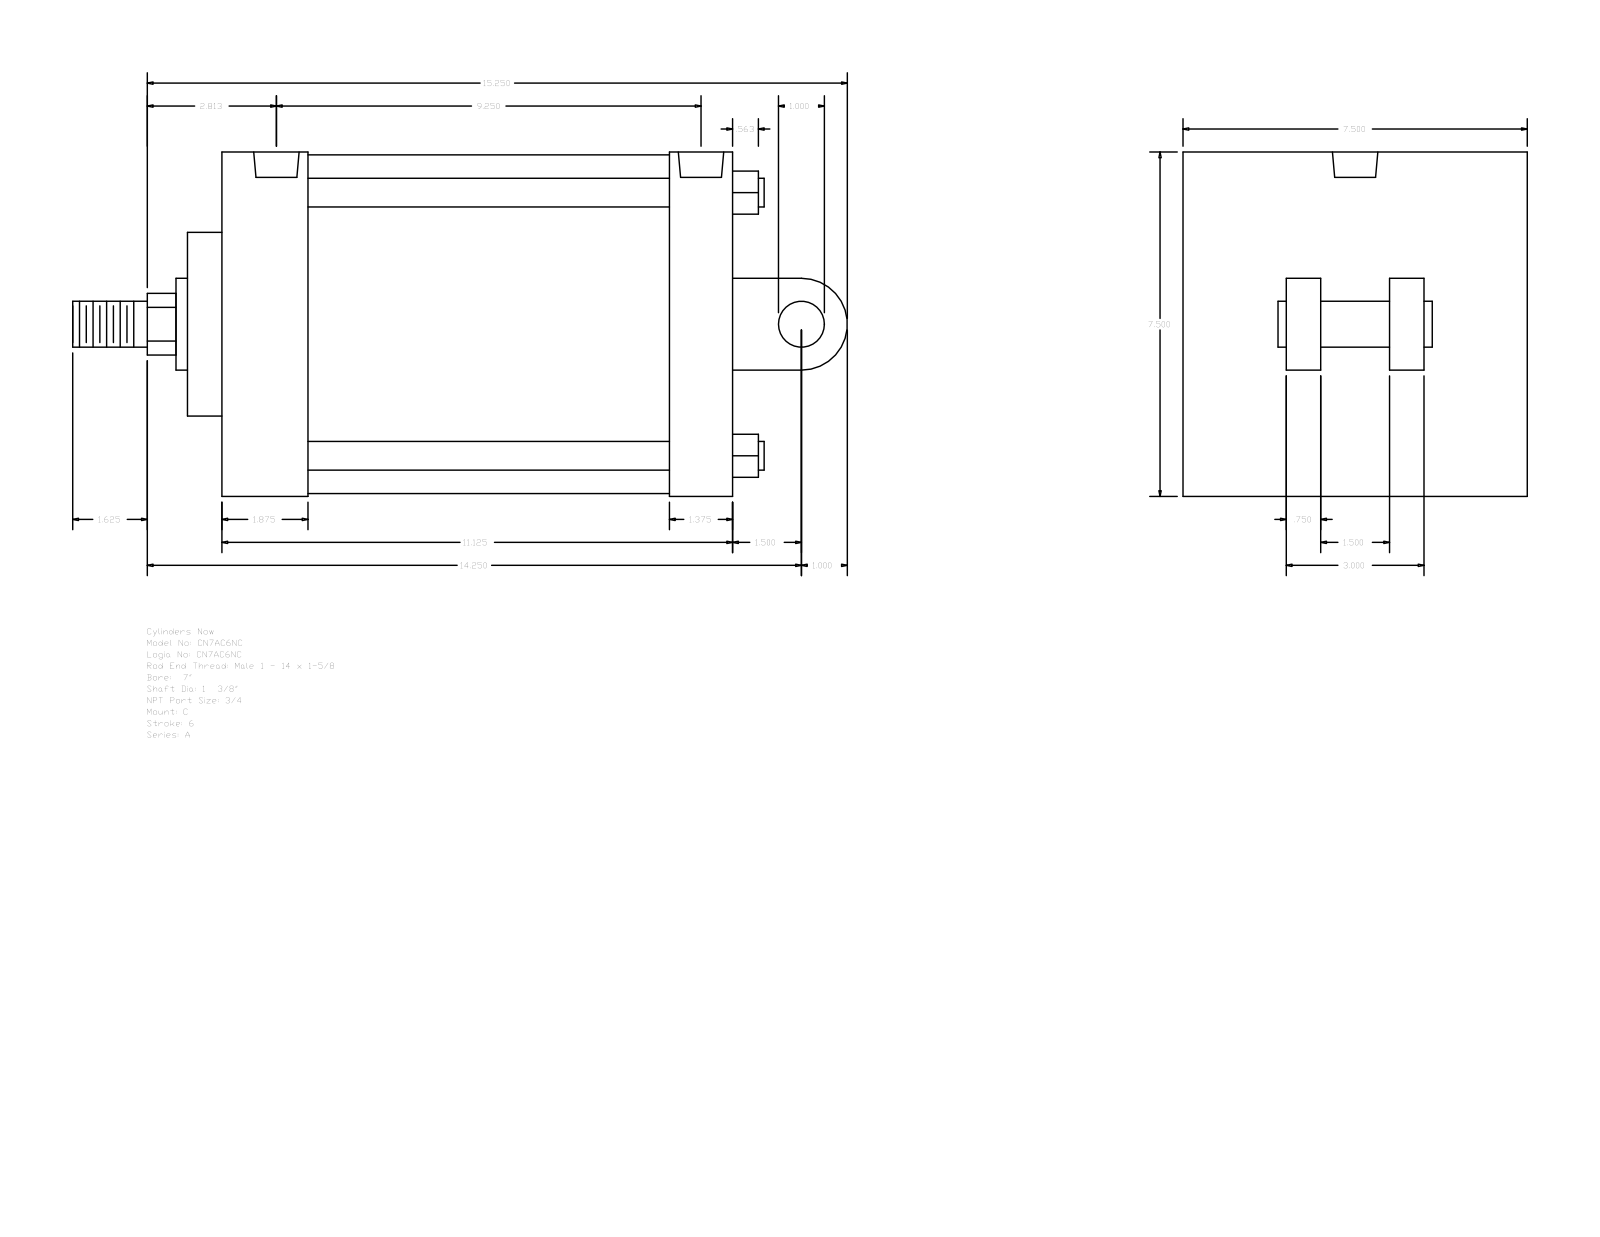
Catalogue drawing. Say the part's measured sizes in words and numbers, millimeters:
The part is named "A_C__0700_1.375". Its 3-D file was written by "GSSL Pune (CONFIG_CONTROL_DESIGN)". It is 0 solids with 104 faces: 75 planar, 29 cylindrical and 0 other. Overall it measures 428.62 by 190.5 by 190.5 millimeters. Round holes: 4 of diameter 15.08, 2 of diameter 25.12. Round bosses or shafts: 4 of diameter 15.88, 2 of diameter 25.4, 1 of diameter 187.32, 1 of diameter 50.8, 1 of diameter 34.92. Partial cylindrical surfaces (rounded edges, fillets, slot ends): 1 of radius 17.06, 1 of radius 25.4. The main face-to-face distances are 190.5, 282.58, 76.2, 57.15, 19.04, 301.62, 66.67, 47.63, 234.95, 266.7. The hole center spacings are 5.56, 223.83, 229.39, 234.95.
